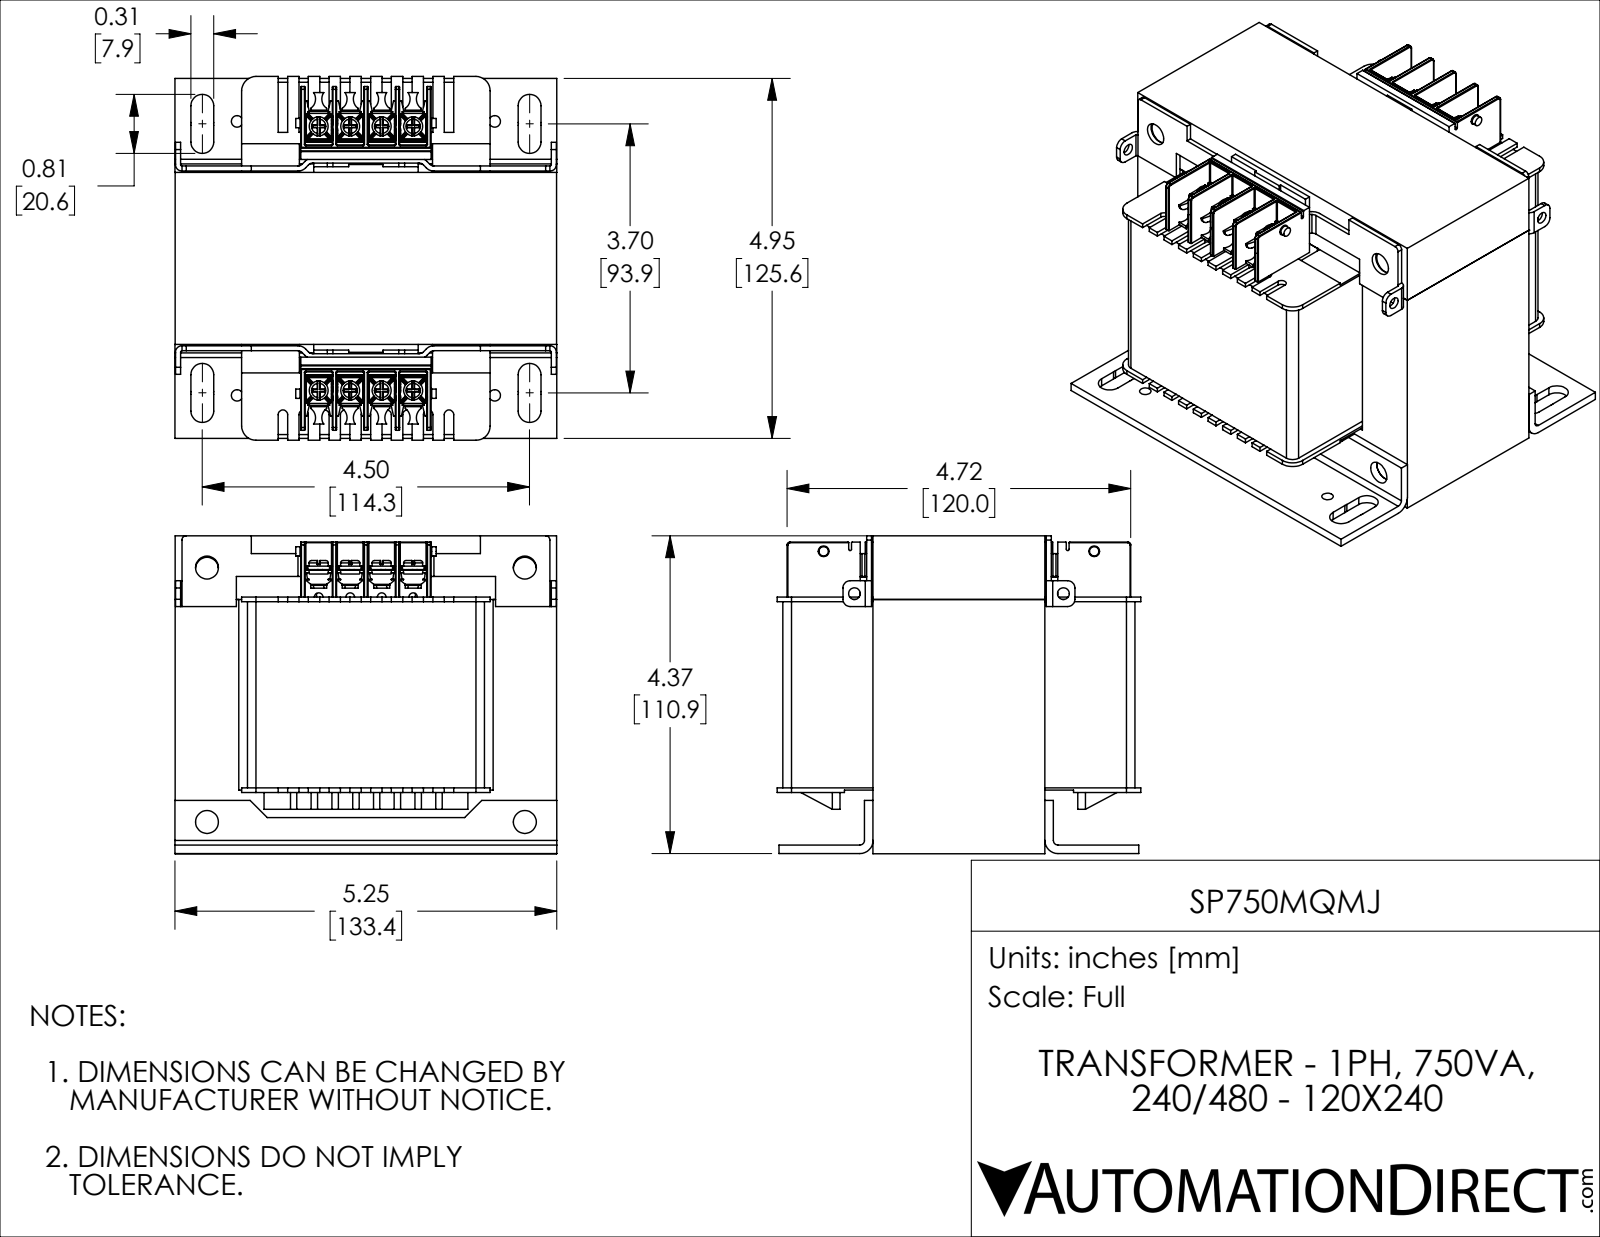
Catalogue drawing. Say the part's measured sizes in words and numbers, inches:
The part is named "SP750MQMJ". Its 3-D file was written by "SolidWorks 2018 (AUTOMOTIVE_DESIGN)". It is 42 solids with 3368 faces: 2121 planar, 949 cylindrical and 298 other. Overall it measures 5.25 by 5 by 4.371 inches. Its volume is 73.28 cubic inches and its surface area 342.9 square inches. Round holes: 13 of diameter 0.157, 8 of diameter 0.105, 8 of diameter 0.138, 6 of diameter 0.315, 2 of diameter 0.161, 2 of diameter 0.177. Round bosses or shafts: 8 of diameter 0.262, 8 of diameter 0.24, 8 of diameter 0.168, 8 of diameter 0.11, 2 of diameter 0.128. Partial cylindrical surfaces (rounded edges, fillets, slot ends): 52 of radius 0.005, 52 of radius 0.01, 42 of radius 0.012, 32 of radius 0.029, 20 of radius 0.157, 12 of radius 0.035, 10 of radius 0.079, 9 of radius 0.065. The main face-to-face distances are 0.874, 3.496, 0.118, 4.37, 2.362, 0.992, 4.252, 1.748, 1.24, 2.622. The hole center spacings are 0.433, 0.866, 3.646, 1.299, 3.62, 3.722, 3.636, 3.656.
